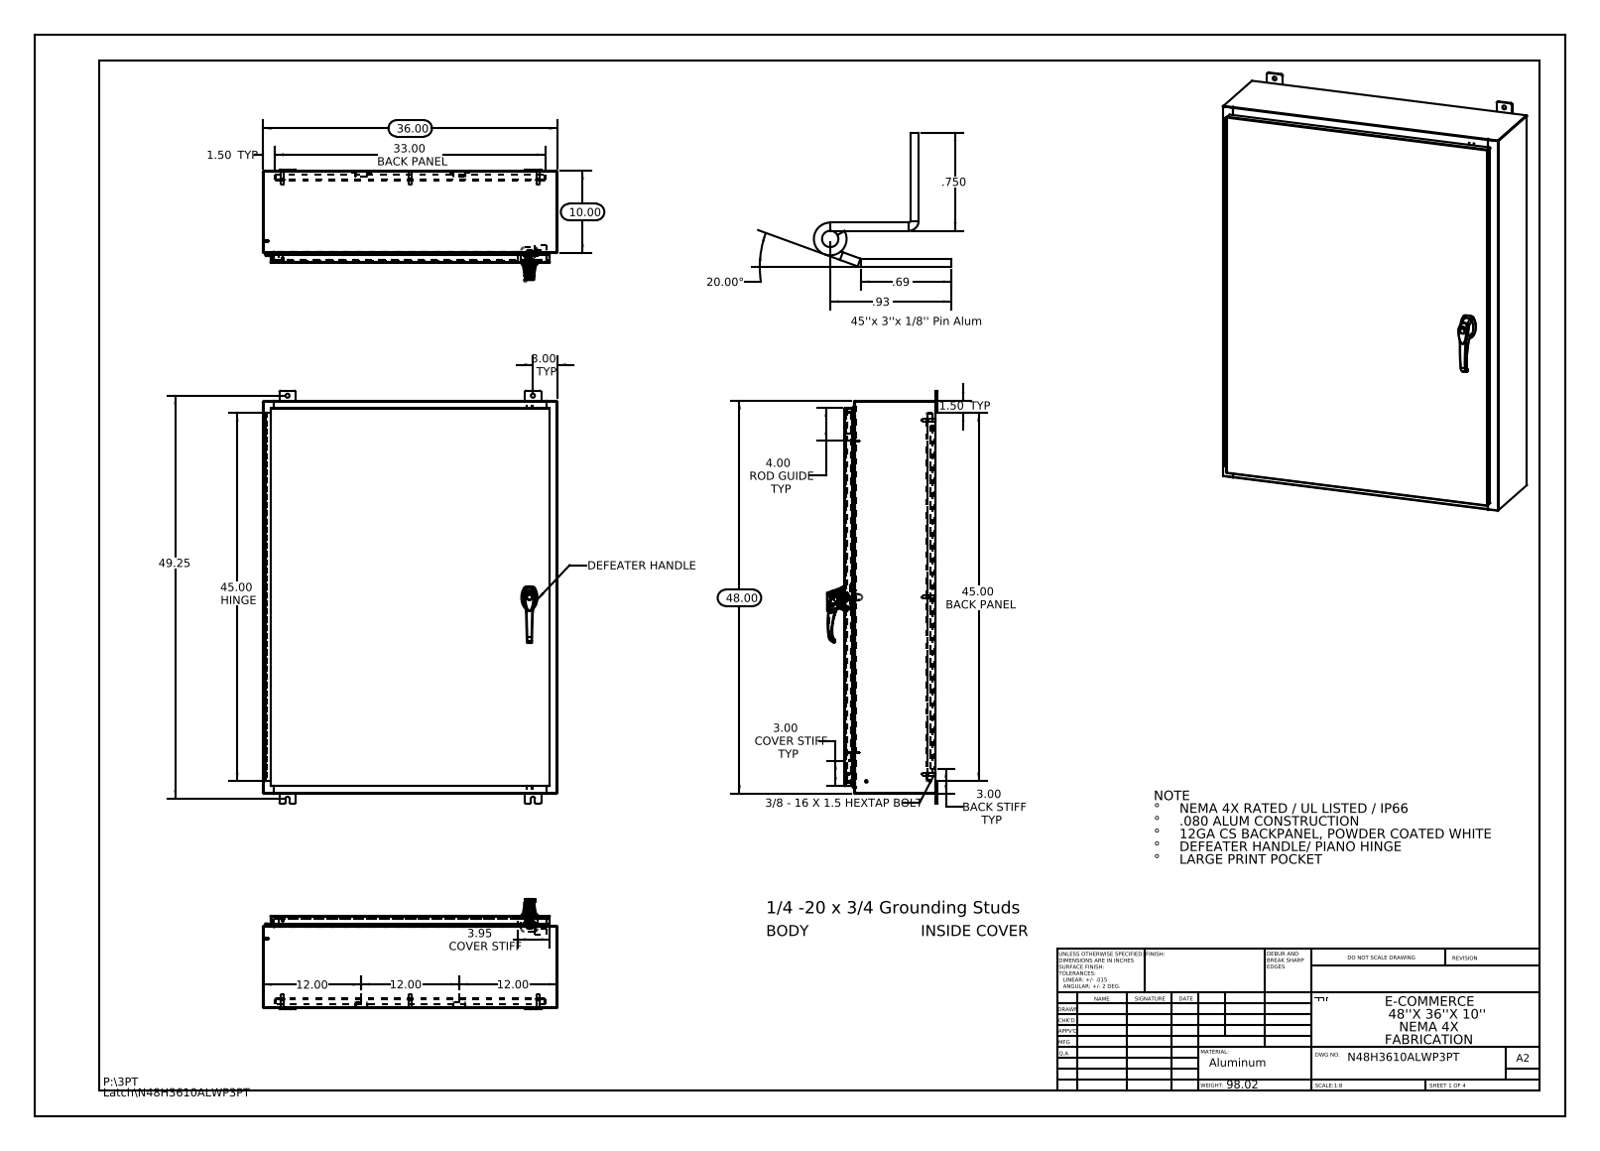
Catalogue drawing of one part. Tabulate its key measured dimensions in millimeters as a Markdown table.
| quantity | value |
| --- | --- |
| part name | 2616310101; N48H3610ALWP3PT Defeater Handle - 3 - 2500-51 ZN; 10_30 CD Stud; 21130102 (+8 more) |
| STEP written by | SolidWorks 2013 (CONFIG_CONTROL_DESIGN) |
| units | millimeters |
| bodies | 51 solids, 3400 faces (1309 planar, 1305 cylindrical, 786 other) |
| overall size | 1282.7 × 914.4 × 342.8 |
| volume | 10 340 000 mm³ |
| surface area | 10 090 000 mm² |
| round holes (diameter × count) | 12.7 × 12, 6.4 × 10, 3.5 × 3, 4.1 × 3, 2 × 2, 5.2 × 2, 8 × 2, 11.1 × 2, 3.2 × 1, 3.2 × 1, 5 × 1, 7 × 1 |
| round bosses / shafts (diameter × count) | 4 × 10, 3.6 × 10, 15.9 × 8, 9.5 × 8, 8.4 × 8, 8 × 3, 6 × 3, 30 × 1 |
| partial cylindrical surfaces (radius × count) | 3 × 37, 0.3 × 34, 0.2 × 33, 2.2 × 28, 4.8 × 24, 1 × 15, 0.7 × 12, 0.2 × 6 |
| main face-to-face distances | 1.9, 282.6, 280.7, 284.5, 2.6, 25.4, 257.2, 27.3, 255.3, 29.9 |
| hole center spacings | 440.9, 499.5, 549.3, 965.3, 1168, 793.8, 1098.6, 7.5 |
